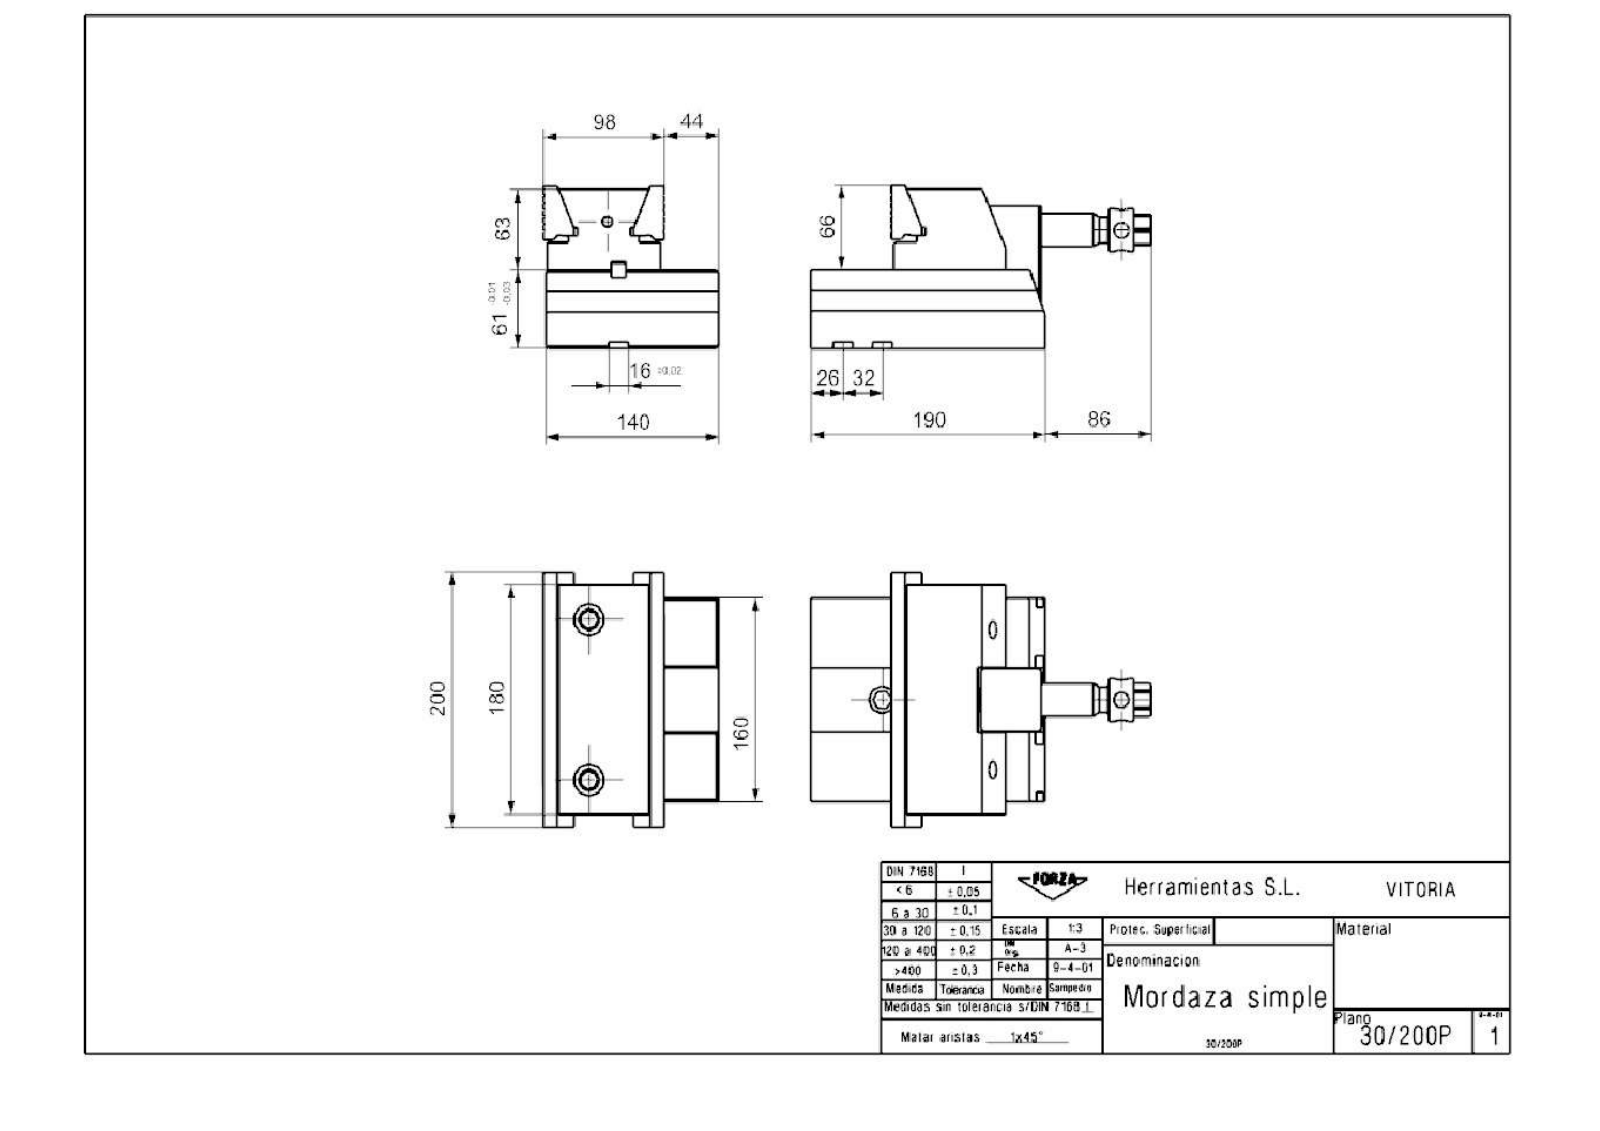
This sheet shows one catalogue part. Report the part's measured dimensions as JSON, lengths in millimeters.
{"part_name": "30_200P_Mordaza", "step_written_by": "SIEMENS PLM Software NX 9.0 (CONFIG_CONTROL_DESIGN)", "units": "millimeters", "bodies": {"solids": 14, "faces": 714, "planar": 452, "cylindrical": 205, "other": 57}, "overall_size": [493.19, 200, 127.55], "volume_mm3": 4621000, "surface_area_mm2": 569171, "round_holes": [[5.19, 11], [15, 9], [8.78, 5], [6.99, 4], [14.38, 4], [23, 4], [10.58, 3], [13, 3], [19, 3], [8.5, 2], [9, 2], [9.5, 2]], "round_bosses_or_shafts": [[34, 1], [33.8, 1], [26, 1], [20, 1], [16.5, 1]], "partial_cylinders_radius": [[0.4, 36], [8, 10], [20, 4], [6, 3], [1.6, 2], [6.5, 2], [4, 1], [7.5, 1]], "face_to_face_distances": [61.3, 10, 124.3, 63, 61.6, 60.1, 55, 170, 32, 65], "hole_center_spacings": [102, 8.01, 18, 24.52, 33.24, 48, 51.26, 94]}
